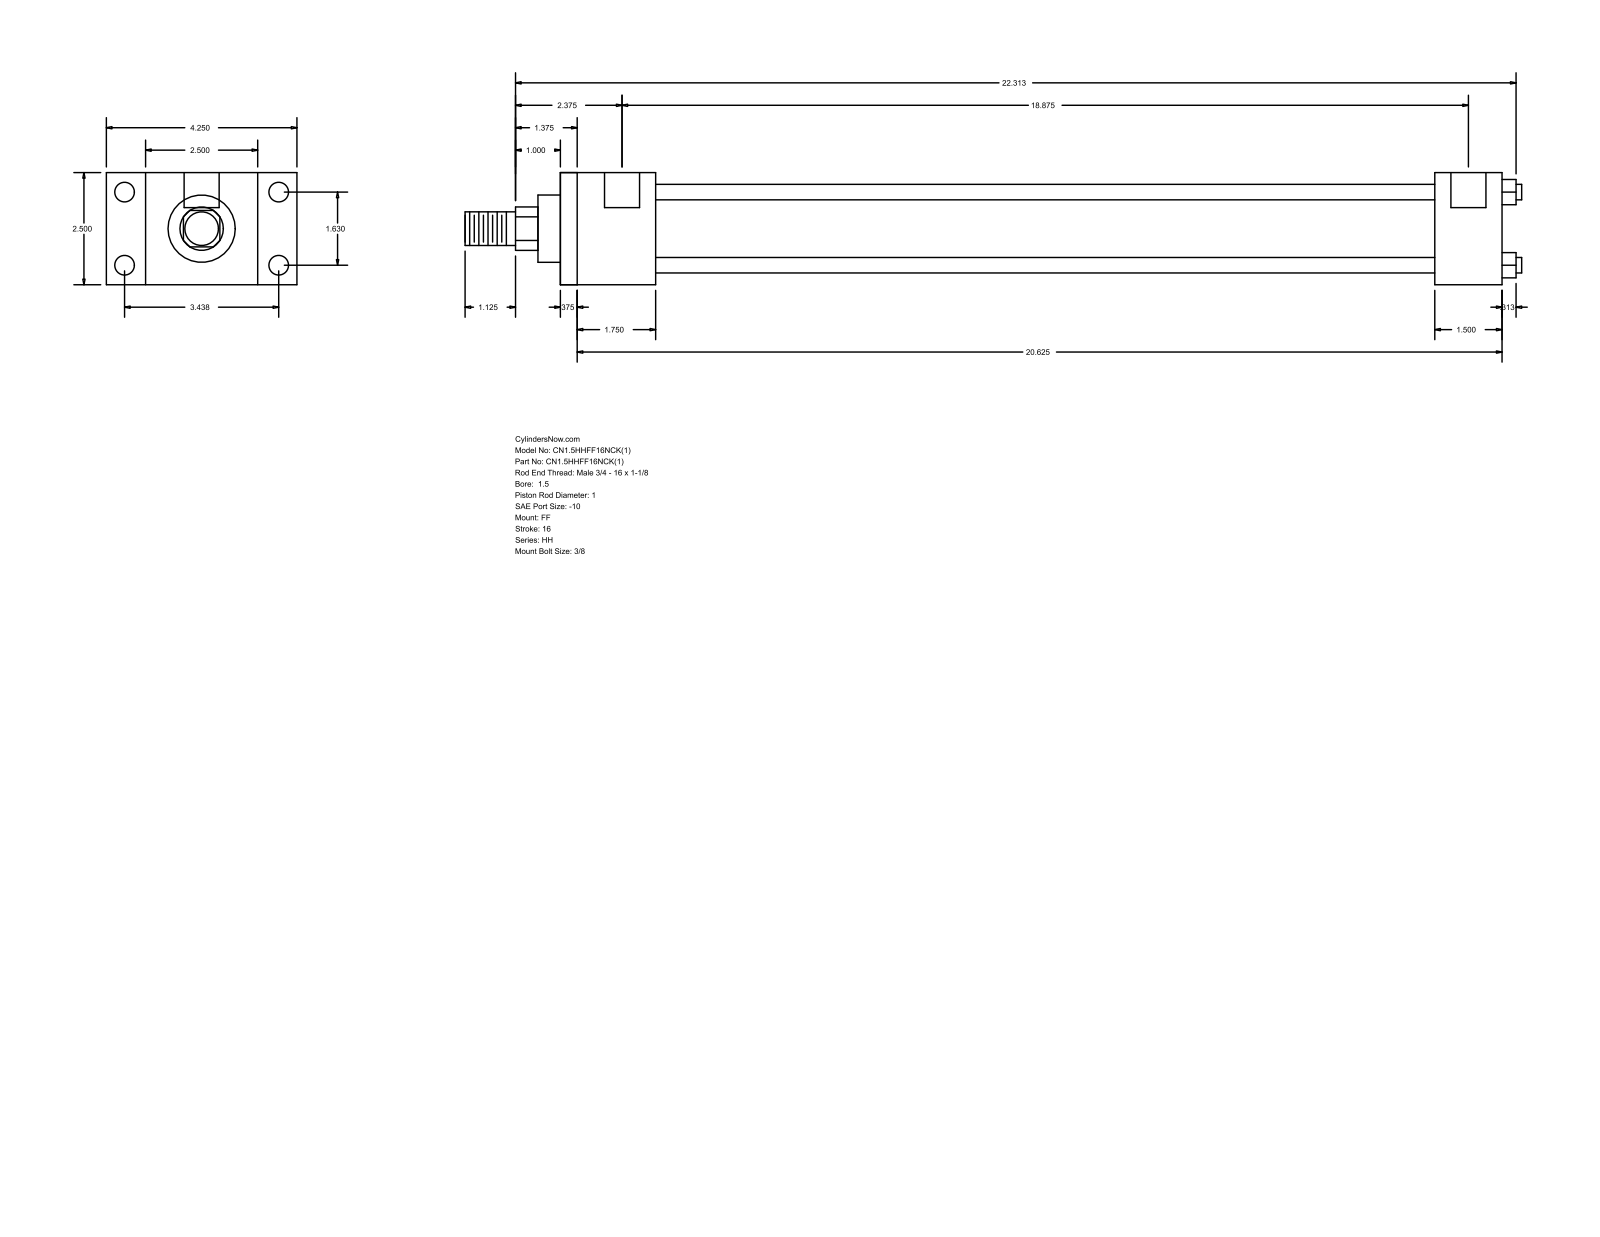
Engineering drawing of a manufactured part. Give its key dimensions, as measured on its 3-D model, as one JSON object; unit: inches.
{"part_name": "HH_FF__0150_1", "step_written_by": "GSSL Pune (CONFIG_CONTROL_DESIGN)", "units": "inches", "bodies": {"solids": 0, "faces": 92, "planar": 64, "cylindrical": 28, "other": 0}, "overall_size": [23.563, 4.25, 2.5], "round_holes": [[0.219, 4], [0.438, 4], [0.781, 2]], "round_bosses_or_shafts": [[0.345, 4], [1.75, 1], [1.5, 1], [1, 1], [0.75, 1]], "partial_cylinders_radius": [[0.484, 1]], "face_to_face_distances": [2.5, 21, 0.375, 20.625, 1.5, 2.125, 1.75, 18.875, 19.5, 19.125], "hole_center_spacings": [0.063, 1.63, 3.438, 3.805, 18.937, 19, 18.875]}
